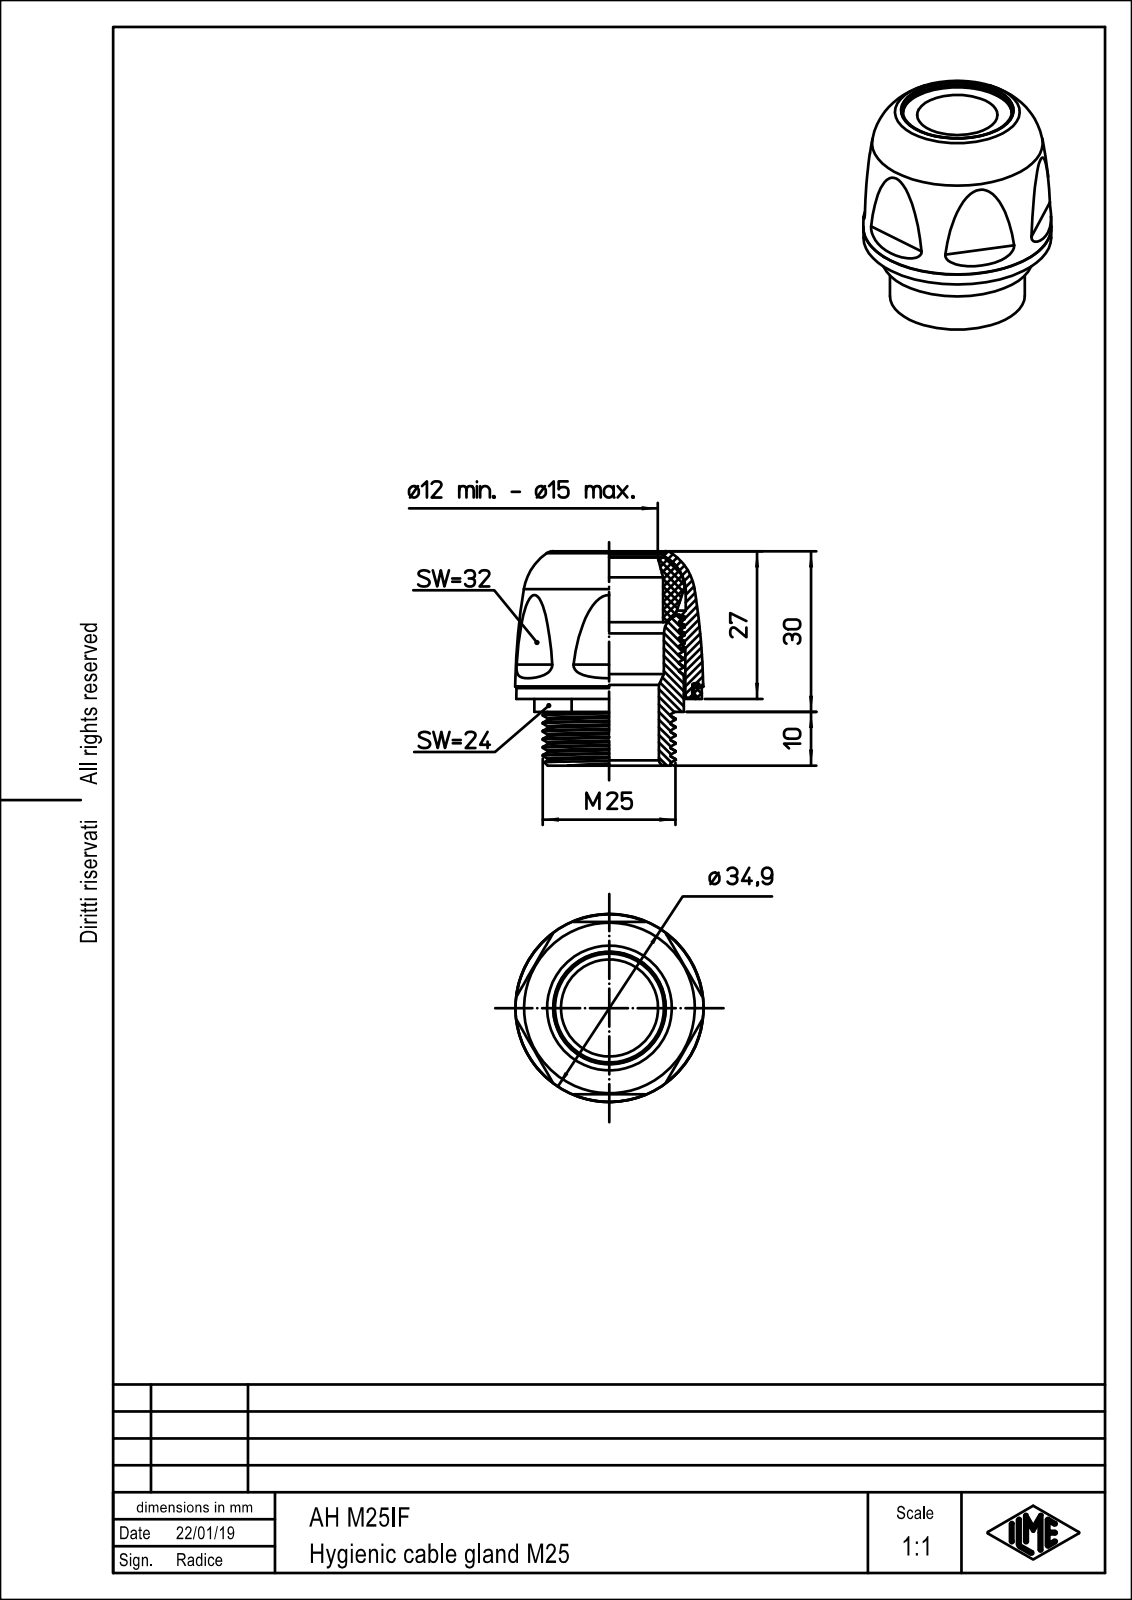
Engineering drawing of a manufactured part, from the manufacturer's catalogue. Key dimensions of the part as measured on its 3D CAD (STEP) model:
Part name (STEP PRODUCT): AH_M25IF
STEP written by: PTC Creo Elements/Direct Modeling 19.0E 27-Jun-2016 (C) Parametric Technology GmbH (AUTOMOTIVE_DESIGN)
Units: millimetres
Bodies: 1 solid, 43 faces (13 planar, 16 cylindrical, 14 other)
Overall size (bounding box): 39.78 × 34.9 × 34.9
Volume: 21 718 mm³ · Surface area: 6 839 mm²
Round holes (diameter × count): ⌀14.9 ×1, ⌀15 ×1, ⌀20.2 ×1
Round bosses / shafts (diameter × count): ⌀28 ×1, ⌀25 ×1
Partial cylindrical surfaces — rounded edges, fillets, slot ends (radius × count): R3 ×6
Main face-to-face distances: 32, 12.5, 38.8, 26.3, 8, 4.5, 30.8, 39.79, 31.79, 27.29
